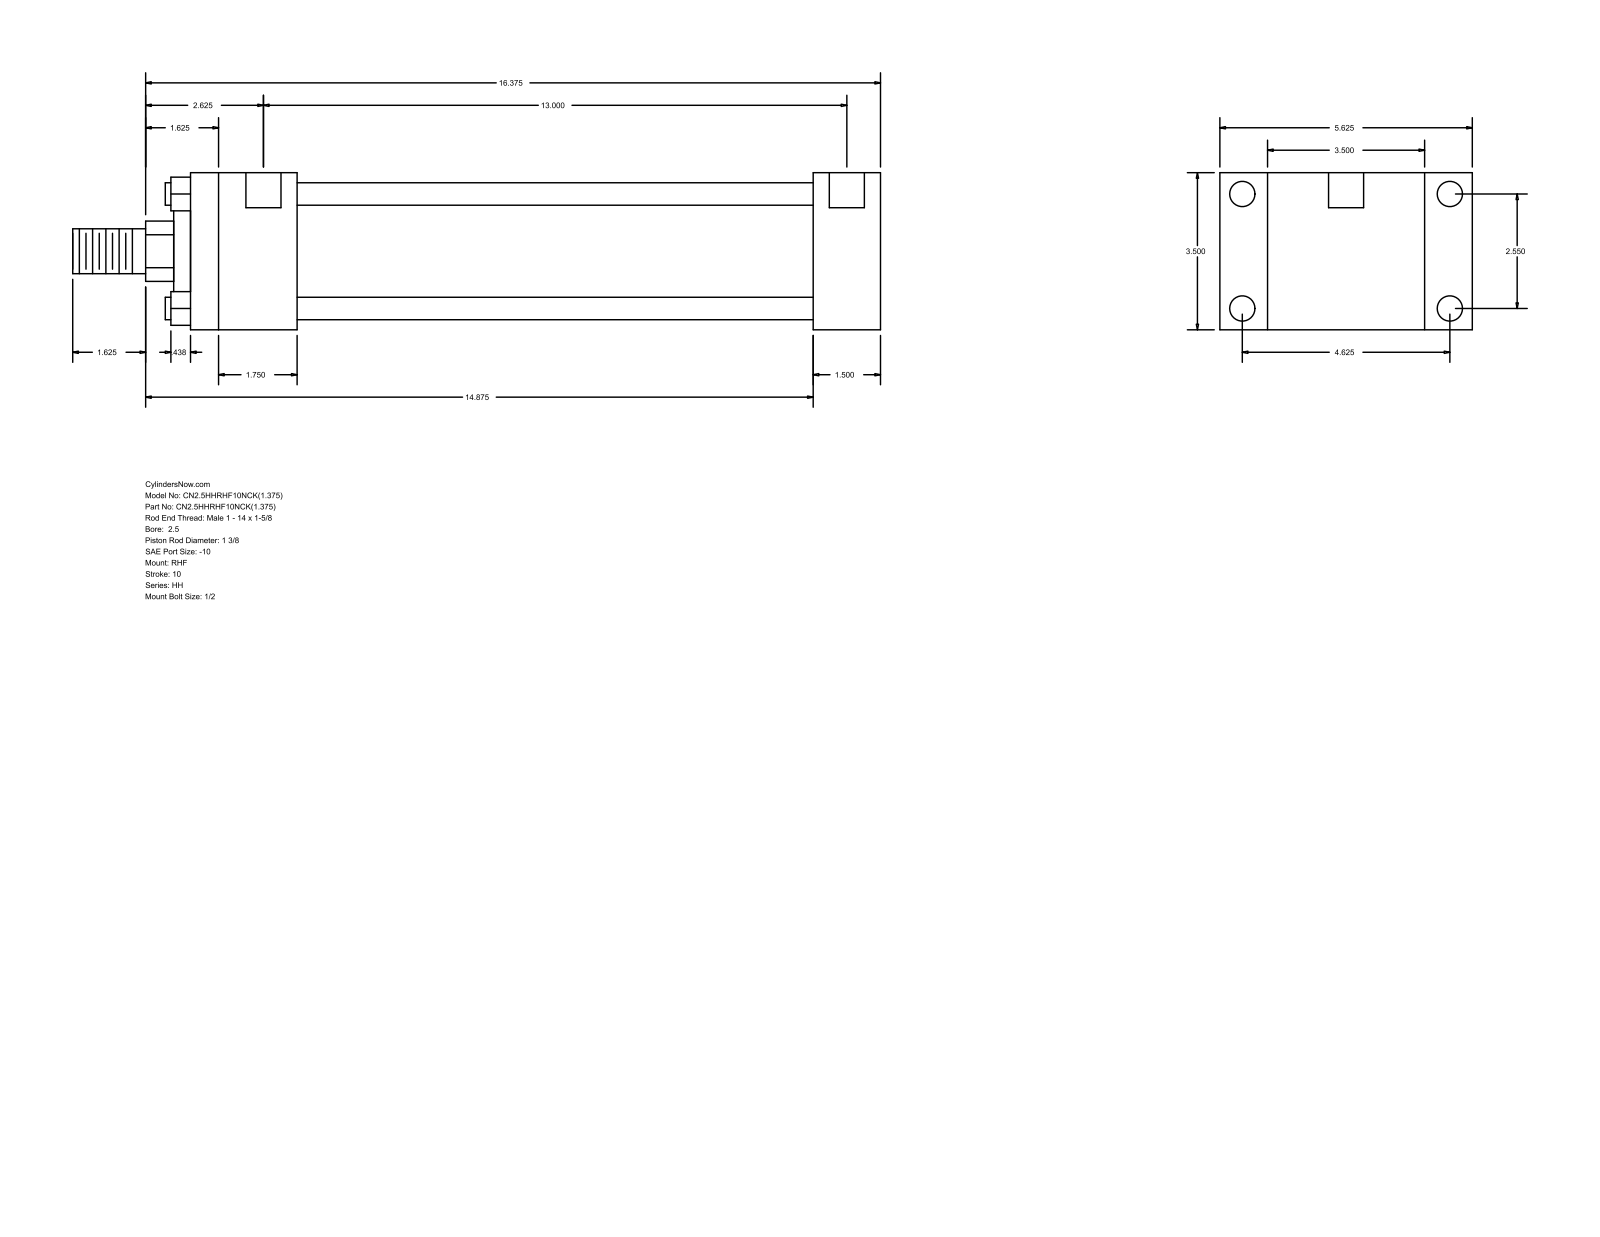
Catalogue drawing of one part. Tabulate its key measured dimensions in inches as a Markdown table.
| quantity | value |
| --- | --- |
| part name | HH_RHF__0250_1.375 |
| STEP written by | GSSL Pune (CONFIG_CONTROL_DESIGN) |
| units | inches |
| bodies | 0 solids, 88 faces (60 planar, 28 cylindrical, 0 other) |
| overall size | 18 × 5.625 × 3.5 |
| round holes (diameter × count) | 0.219 × 4, 0.563 × 4, 0.781 × 2 |
| round bosses / shafts (diameter × count) | 0.5 × 4, 2.875 × 1, 2 × 1, 1.375 × 1, 1 × 1 |
| partial cylindrical surfaces (radius × count) | 0.672 × 1 |
| main face-to-face distances | 3.5, 1.5, 1.063, 4.563, 13.875, 15.375, 5.625, 2.375, 11.5, 13 |
| hole center spacings | 0.062, 2.55, 4.625, 5.281, 13.063, 13.125, 13 |
